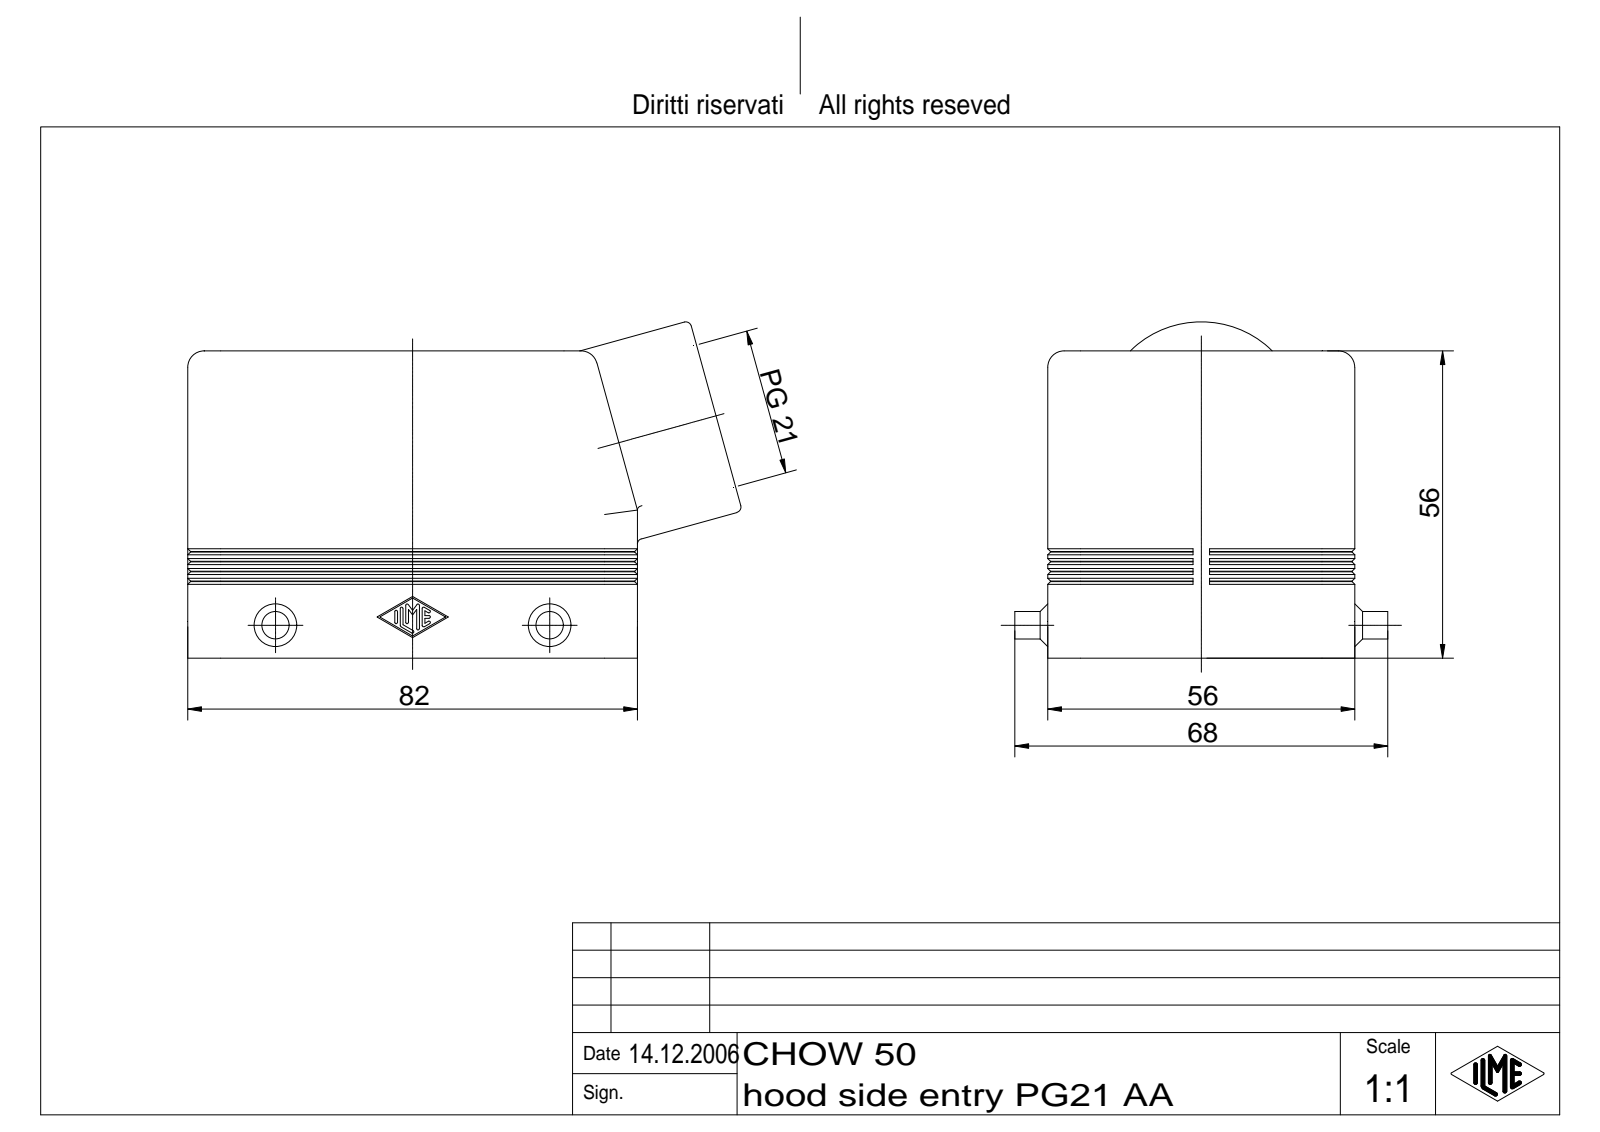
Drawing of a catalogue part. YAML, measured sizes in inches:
part_name: "CHOW 50"
step_written_by: "Autodesk Inventor 7 (AUTOMOTIVE_DESIGN)"
units: inches
bodies: {solids: 1, faces: 448, planar: 150, cylindrical: 128, other: 170}
overall_size: [3.972, 2.677, 2.413]
volume: 4.633
surface_area: 64.43
round_holes:
  - {diameter: 0.097, count: 4}
  - {diameter: 0.138, count: 4}
  - {diameter: 0.976, count: 1}
  - {diameter: 1.054, count: 1}
round_bosses_or_shafts:
  - {diameter: 0.197, count: 2}
  - {diameter: 1.417, count: 1}
partial_cylinders:
  - {radius: 0.01, count: 14}
  - {radius: 0.079, count: 8}
  - {radius: 0.118, count: 8}
  - {radius: 0.236, count: 6}
  - {radius: 0.217, count: 2}
  - {radius: 0.63, count: 1}
face_to_face_distances: [0.118, 2.087, 2.205, 1.969, 3.11, 0.443, 2.785, 0.325, 2.667, 3.228]
hole_center_spacings: [0.63, 2.598, 2.674]
